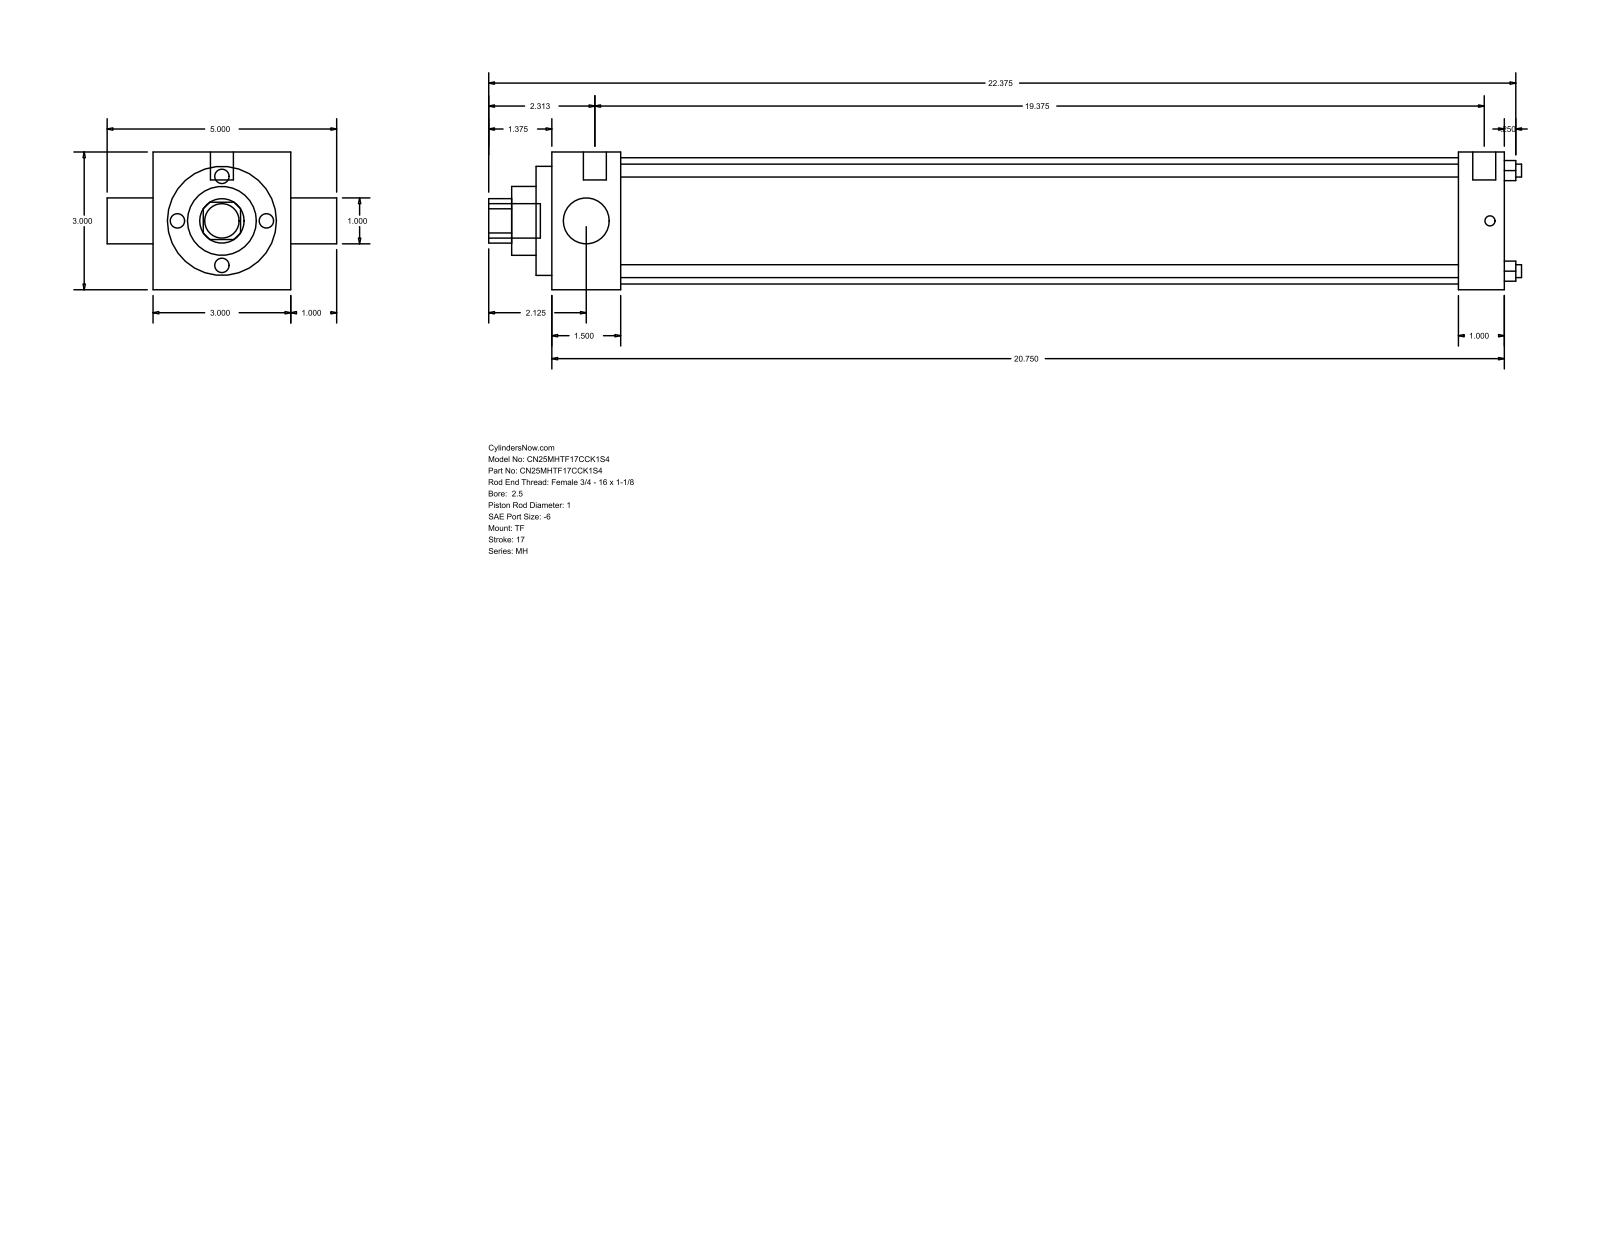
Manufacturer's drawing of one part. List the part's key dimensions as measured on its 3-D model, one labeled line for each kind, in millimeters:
Part name (STEP PRODUCT): MH_TF__0250_1
STEP written by: GSSL Pune (CONFIG_CONTROL_DESIGN)
Units: millimetres
Bodies: 0 solids, 86 faces (61 planar, 25 cylindrical, 0 other)
Overall size (bounding box): 571.5 × 127 × 76.2
Round holes (diameter × count): ⌀7.14 ×4, ⌀25.4 ×2, ⌀38.1 ×1, ⌀60.33 ×1, ⌀69.85 ×1
Round bosses / shafts (diameter × count): ⌀5.56 ×3, ⌀12.7 ×2, ⌀19.05 ×1
Partial cylindrical surfaces — rounded edges, fillets, slot ends (radius × count): R12.29 ×1
Main face-to-face distances: 76.2, 527.06, 25.4, 38.11, 488.95, 501.66, 463.55, 8.73, 46.84, 510.39
Hole centre spacings: 39.33, 55.62, 78.66
